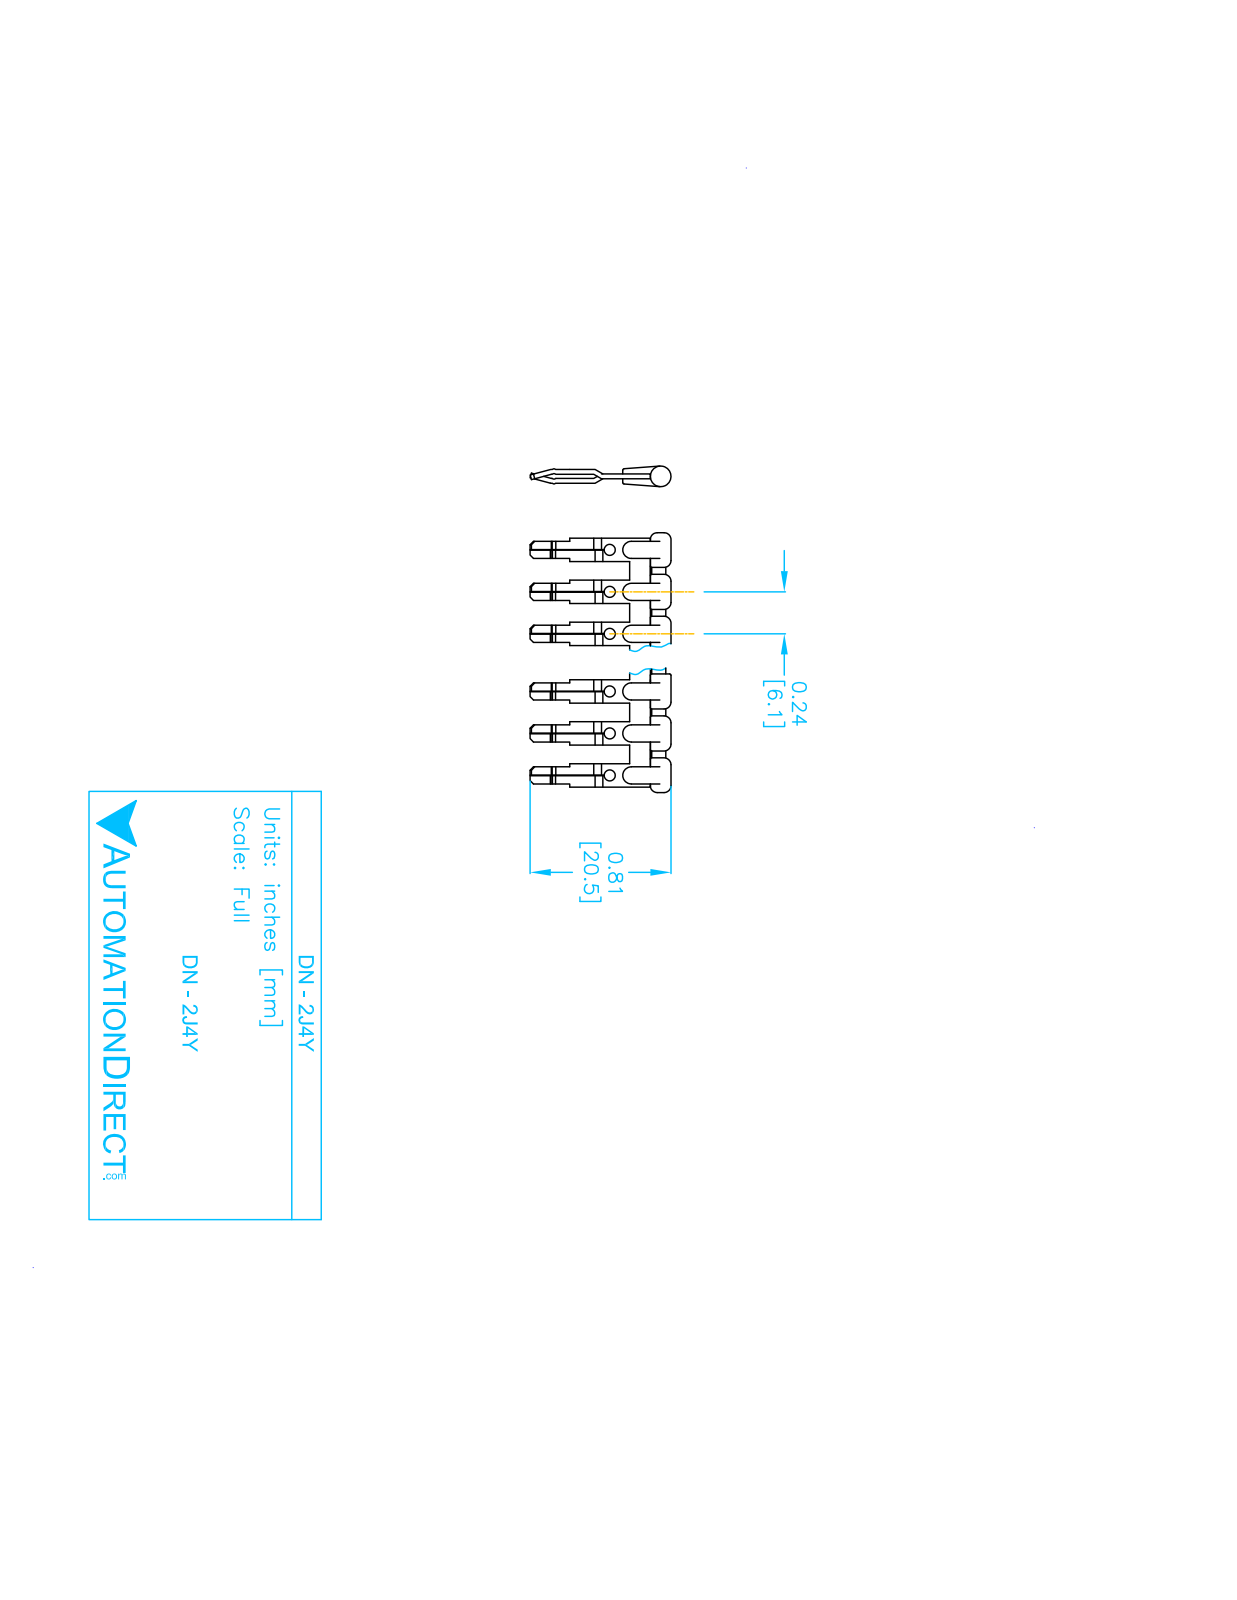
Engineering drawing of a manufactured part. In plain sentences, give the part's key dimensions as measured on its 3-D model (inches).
The part is named "DN-2J4YMN; J4_M; J4PSX_J4 INTERMEDIO". Its 3-D file was written by "SolidWorks 2017 (AUTOMOTIVE_DESIGN)". It is 4 solids with 134 faces: 78 planar, 38 cylindrical and 18 other. Overall it measures 0.801 by 0.437 by 0.118 inches. Its volume is 0.012 cubic inches and its surface area 0.807 square inches. Round holes: 4 of diameter 0.051. Round bosses or shafts: 1 of diameter 0.118. Partial cylindrical surfaces (rounded edges, fillets, slot ends): 8 of radius 0.02, 4 of radius 0.028, 2 of radius 0.049, 1 of radius 0.03. The main face-to-face distances are 0.028, 0.022, 0.071, 0.049, 0.24, 0.043, 0.118, 0.051, 0.067, 0.189. The hole center spacings are 0.162, 0.24, 0.29.
